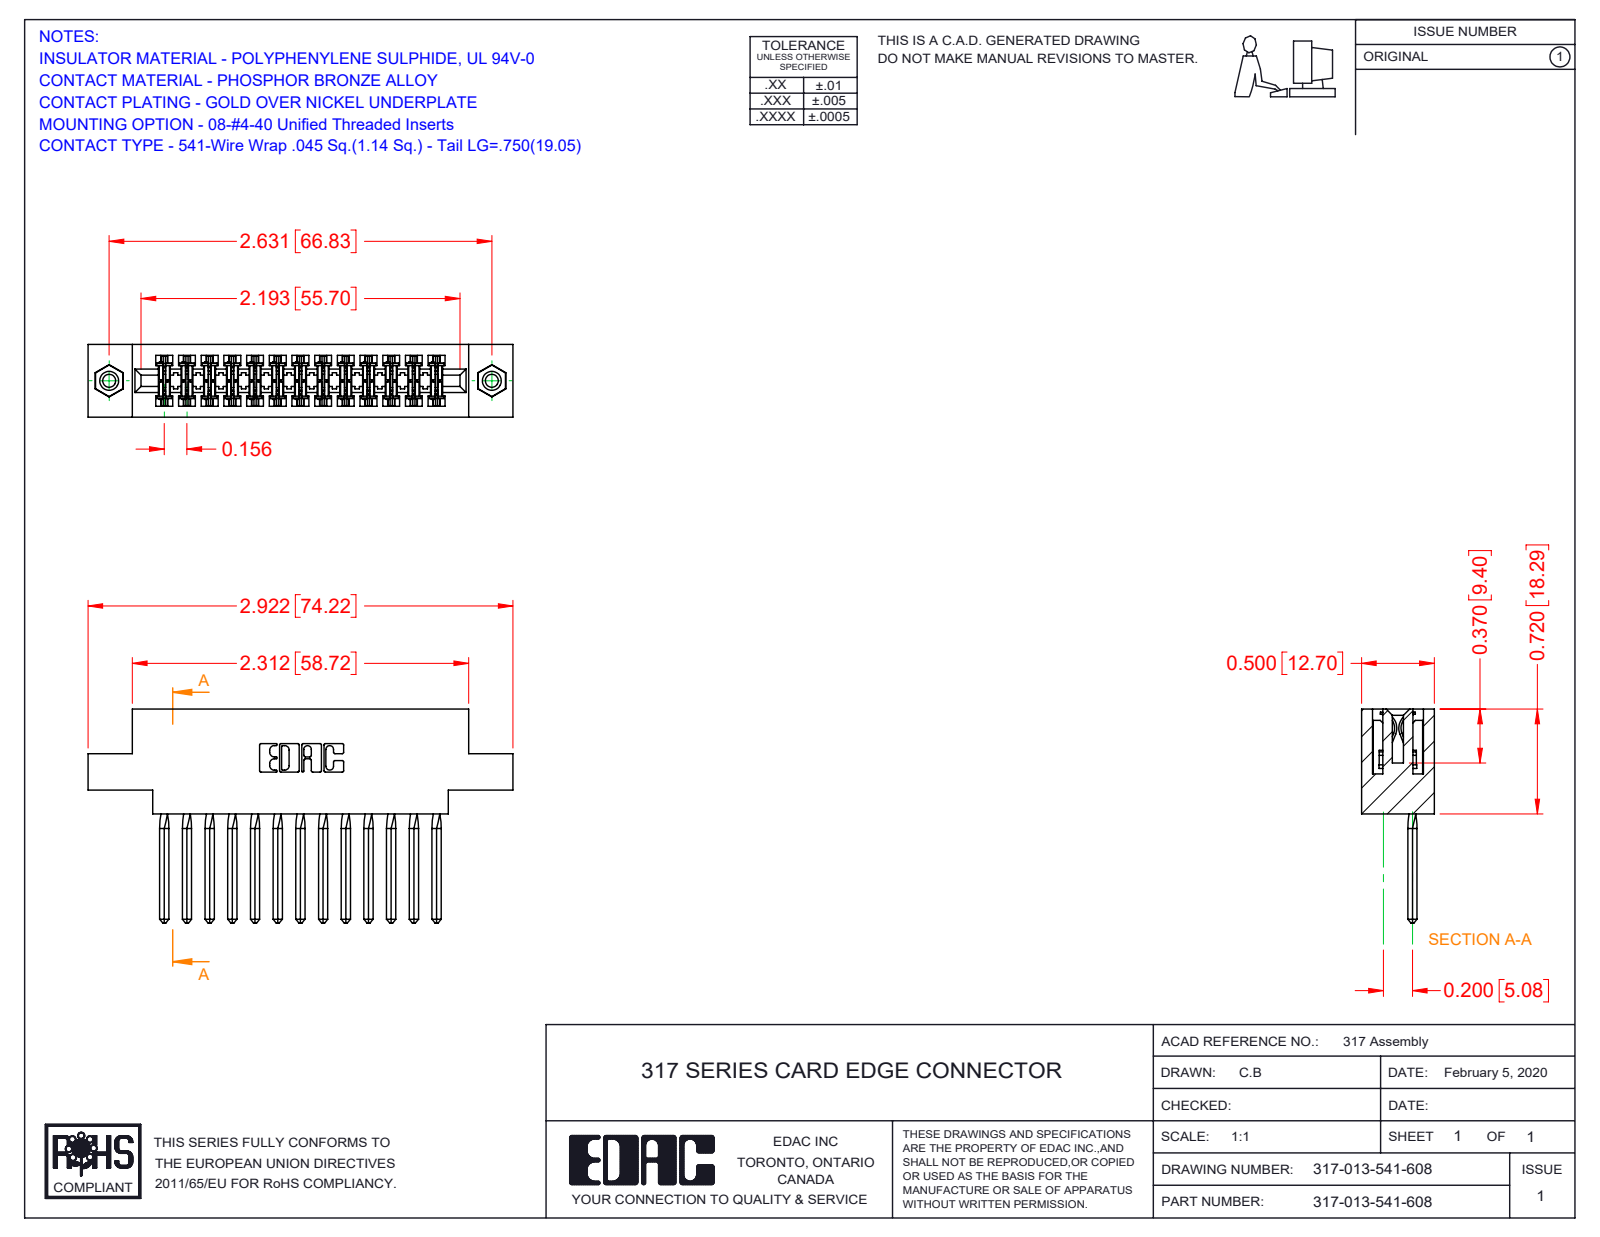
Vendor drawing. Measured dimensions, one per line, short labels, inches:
name: 317 Part_.156 Dia - TI; 317-013-541-678; 317-290-002_541; 345-250-001_345-250-003-102
written by: SolidWorks 2016 (CONFIG_CONTROL_DESIGN)
unit: in
bodies: 16 solids, 2138 faces (1702 planar, 368 cylindrical, 68 other)
size: 2.922 × 1.47 × 0.5
volume: 0.68 in³; area: 22.93 in²
holes: 2× ⌀0.089, 2× ⌀0.125, 2× ⌀0.156
bosses: 2× ⌀0.155
rounds: 26× R0.015, 22× R0.01, 6× R0.007, 6× R0.031, 3× R0.026, 2× R0.095, 2× R0.1, 2× R0.11
face distances: 0.5, 0.075, 0.425, 0.11, 0.22, 0.065, 0.35, 0.331, 0.195, 0.136
hole spacings: 2.631
